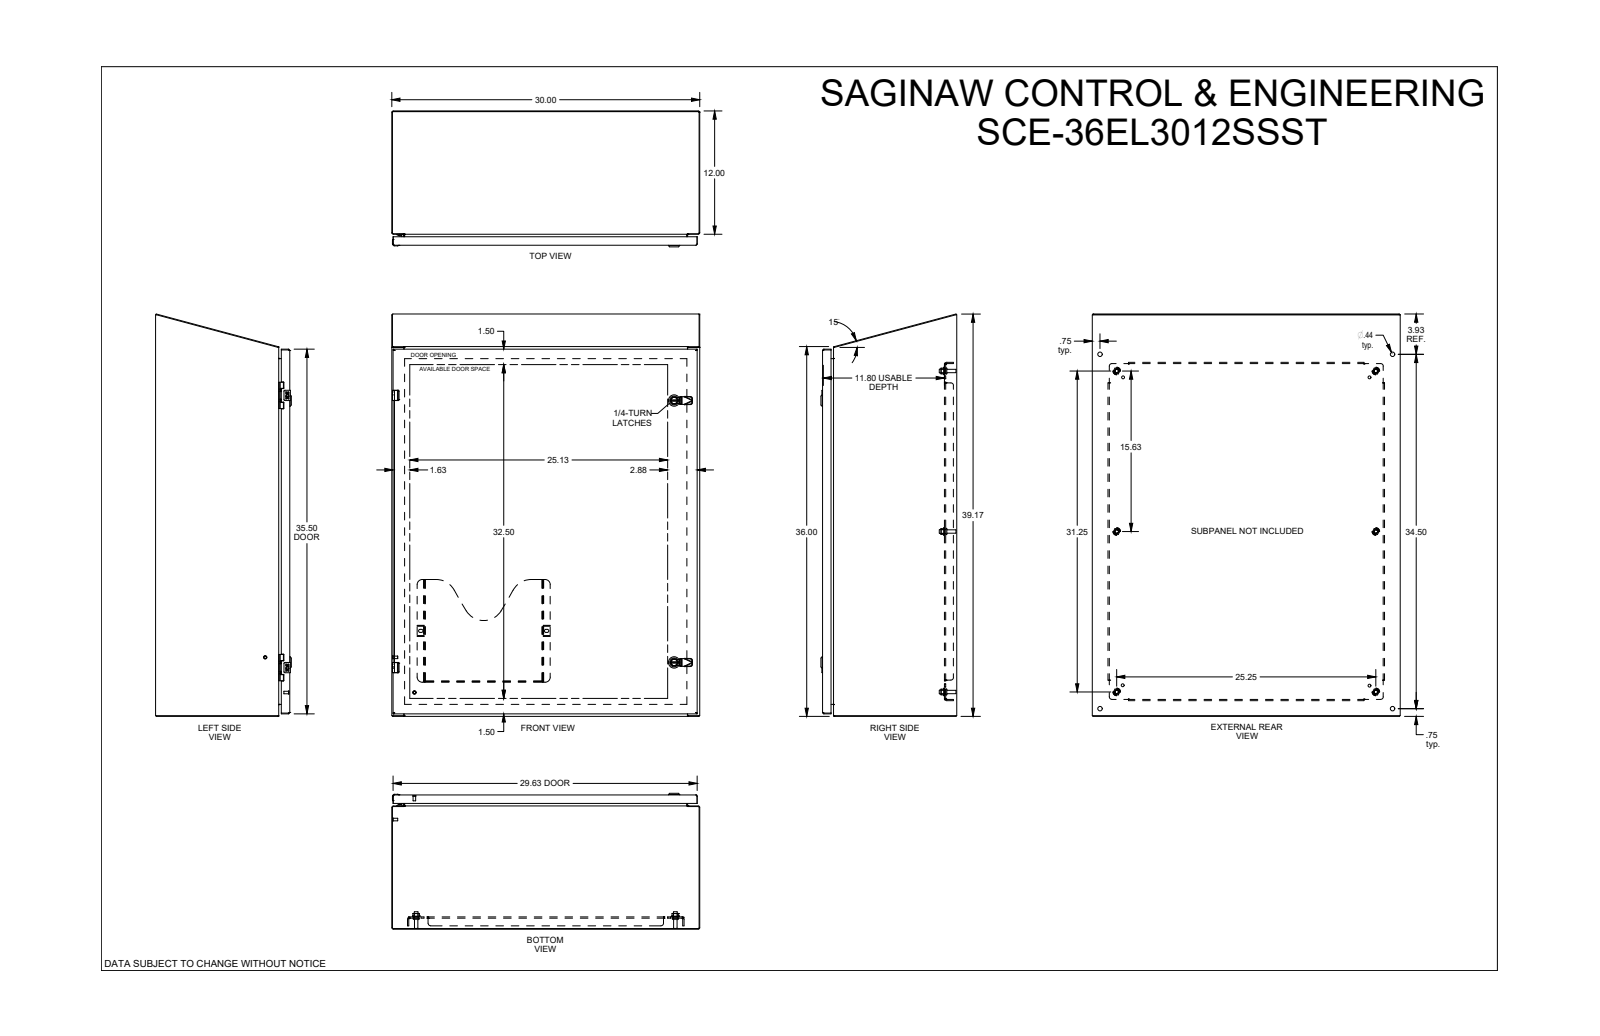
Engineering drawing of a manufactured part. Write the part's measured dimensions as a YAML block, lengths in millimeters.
part_name: "SCE-36EL3012SSST"
step_written_by: "SolidWorks 2019 (CONFIG_CONTROL_DESIGN)"
units: millimeters
bodies: {solids: 0, faces: 2954, planar: 1335, cylindrical: 779, other: 840}
overall_size: [995.1, 762, 336]
round_holes:
  - {diameter: 9.3, count: 6}
  - {diameter: 12.7, count: 6}
  - {diameter: 4.4, count: 4}
  - {diameter: 5.2, count: 4}
  - {diameter: 6.2, count: 4}
  - {diameter: 6.8, count: 4}
  - {diameter: 7.1, count: 4}
  - {diameter: 9.5, count: 4}
  - {diameter: 11.1, count: 4}
  - {diameter: 4, count: 2}
  - {diameter: 5, count: 2}
  - {diameter: 5.5, count: 2}
round_bosses_or_shafts:
  - {diameter: 9.3, count: 6}
  - {diameter: 8.4, count: 6}
  - {diameter: 4.3, count: 6}
  - {diameter: 6.4, count: 4}
  - {diameter: 6.3, count: 4}
  - {diameter: 5, count: 3}
  - {diameter: 28, count: 2}
  - {diameter: 22, count: 2}
partial_cylinders:
  - {radius: 0.3, count: 56}
  - {radius: 0.3, count: 40}
  - {radius: 0.4, count: 28}
  - {radius: 1, count: 23}
  - {radius: 0.5, count: 20}
  - {radius: 1.8, count: 14}
  - {radius: 0.7, count: 12}
  - {radius: 1.5, count: 11}
face_to_face_distances: [1.9, 330.1, 328.2, 1.9, 332.1, 330.1, 30.5, 301.6, 3.2, 25.4]
hole_center_spacings: [25, 673.1, 0.5, 22.2, 58.4, 114.1, 396.9, 440.1]
